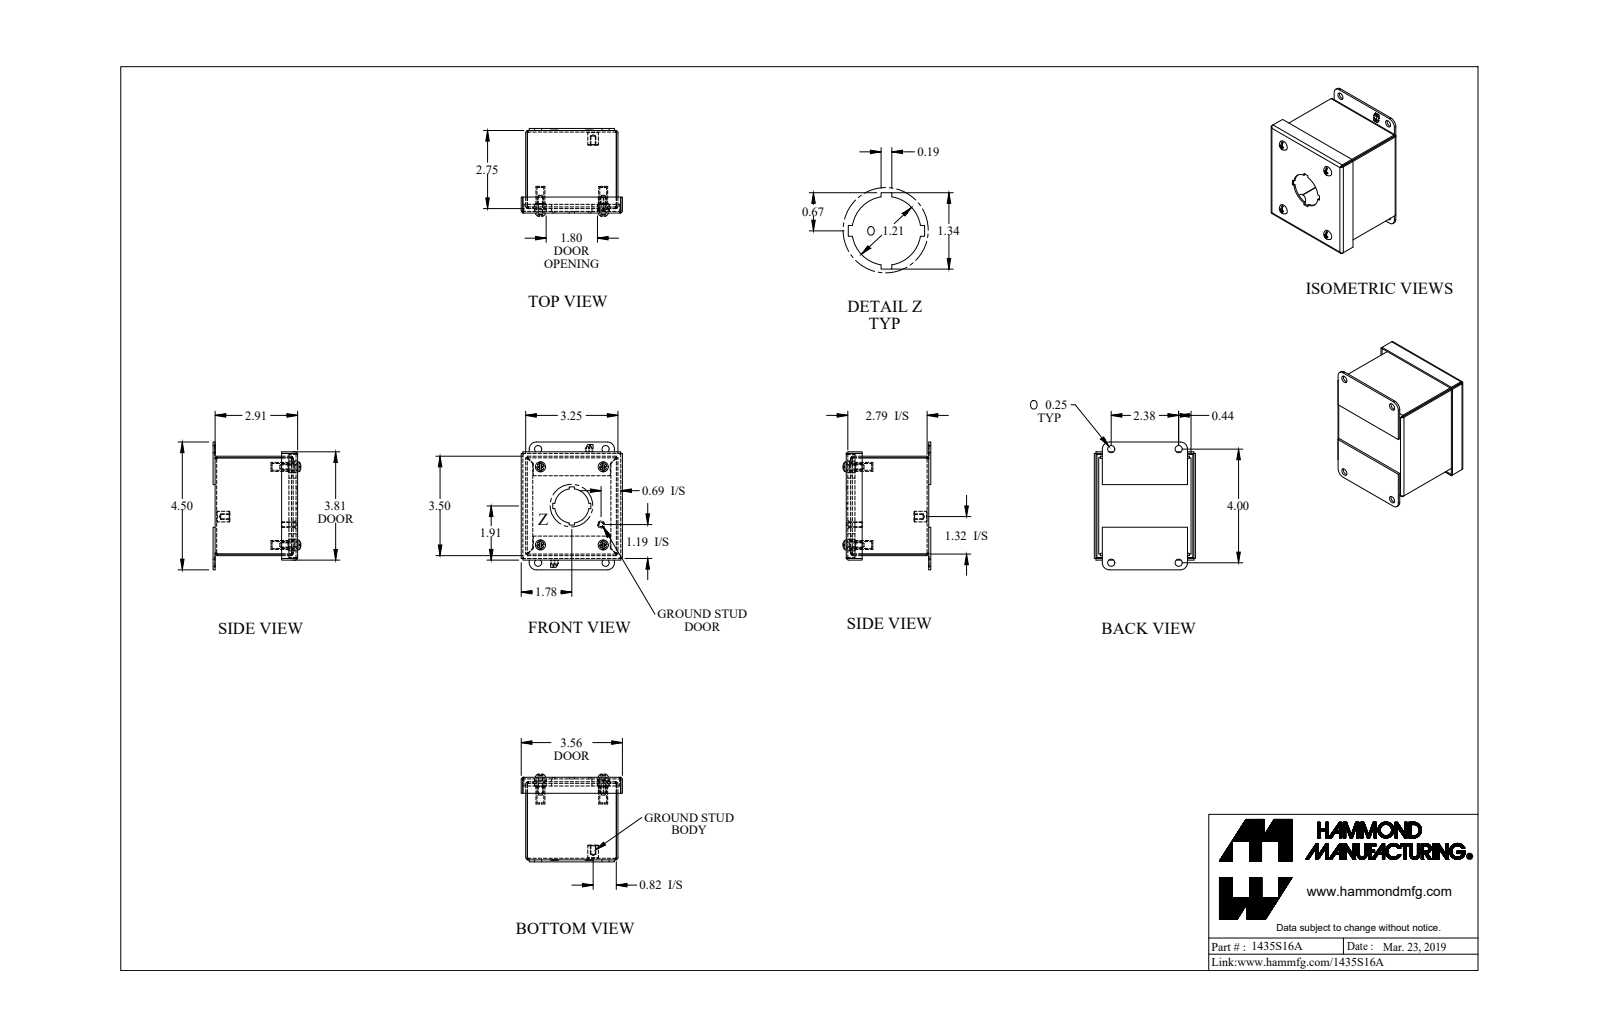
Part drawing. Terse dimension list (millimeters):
name: 1435S16A_Default
written by: SolidWorks 2019 (CONFIG_CONTROL_DESIGN)
unit: mm
bodies: 19 solids, 461 faces (295 planar, 136 cylindrical, 30 other)
size: 114.3 × 90.5 × 78.5
volume: 101 200 mm³; area: 123 000 mm²
holes: 8× ⌀6.4, 4× ⌀1.7, 4× ⌀6.1, 4× ⌀6.4, 4× ⌀10.3, 1× ⌀4, 1× ⌀30.7
bosses: 5× ⌀4.8, 4× ⌀10.3, 4× ⌀8, 4× ⌀3.8, 1× ⌀9.5, 1× ⌀6.4
rounds: 12× R0.7, 12× R2.2, 4× R4.3, 4× R6.4, 2× R3.2
face distances: 1.4, 72.4, 1.4, 81.1, 87.5, 73.8, 70.9, 4, 75.7, 74.2
hole spacings: 56.2, 69.9, 69.9, 16, 56.2, 85.8, 89.6, 103.6
